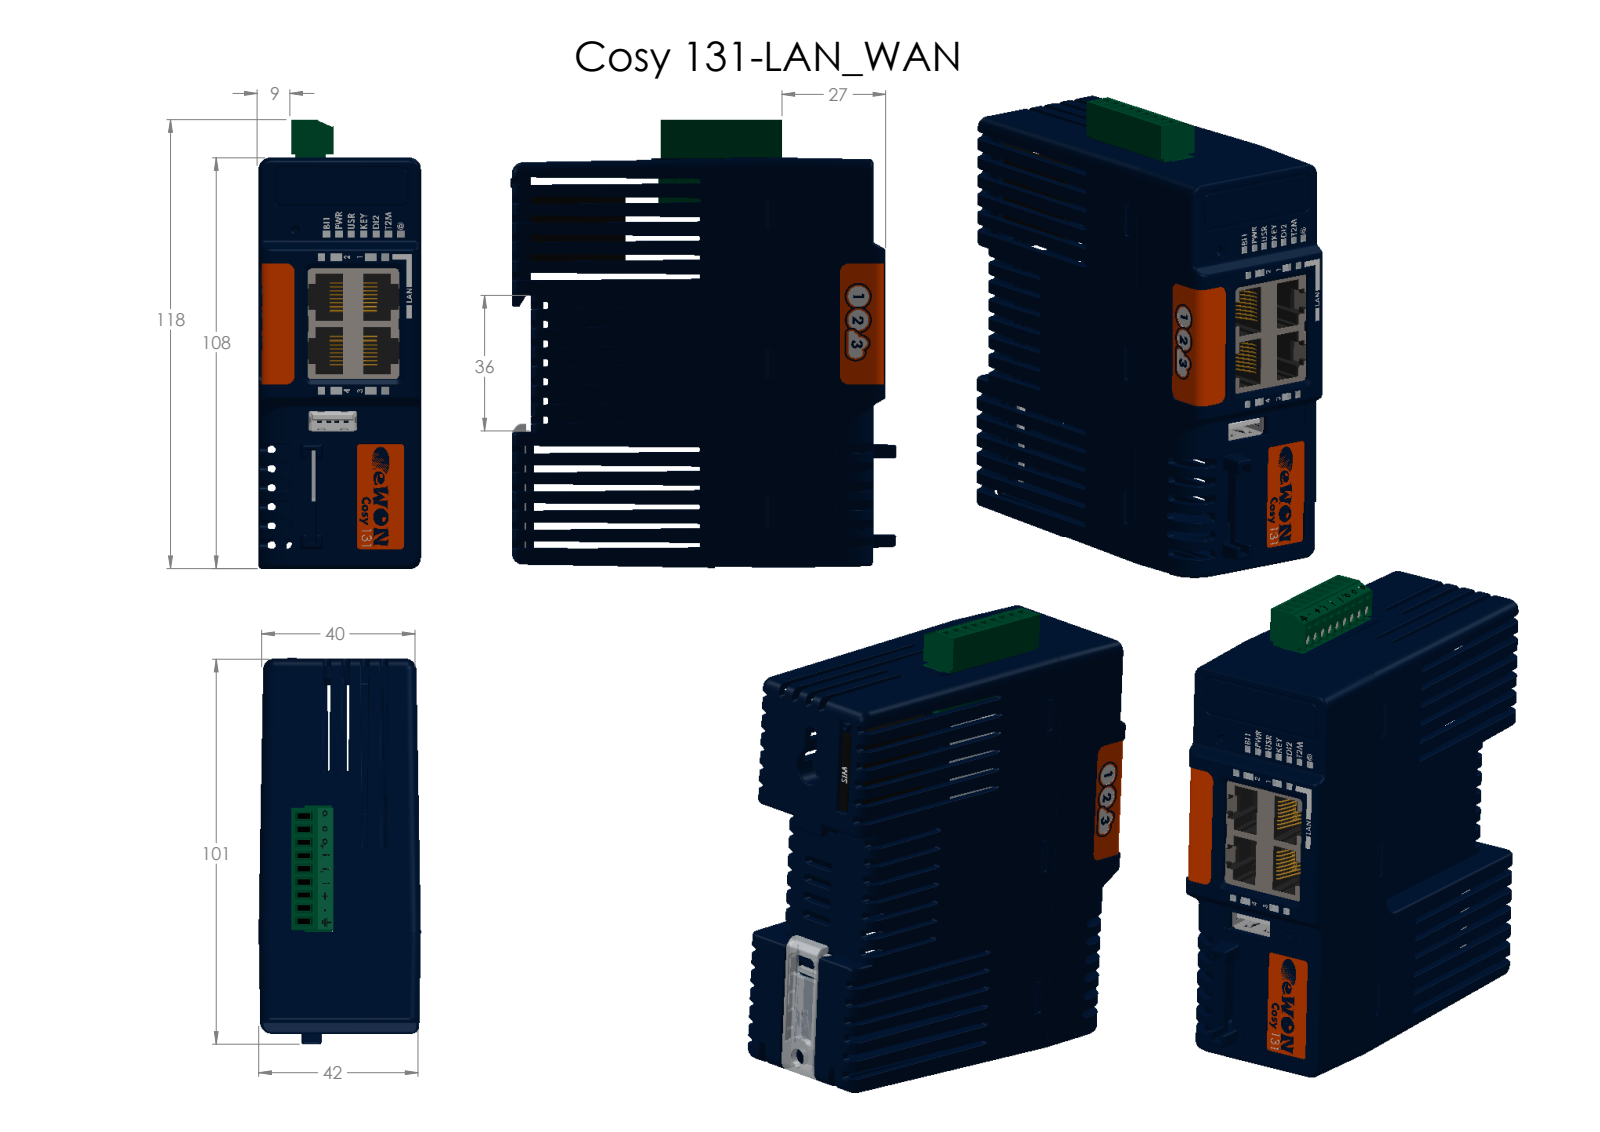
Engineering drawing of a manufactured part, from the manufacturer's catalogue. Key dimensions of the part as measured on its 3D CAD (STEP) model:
Part name (STEP PRODUCT): SIM Tray; COSY 131  LAN_WAN-WIFI_Ethernet COSY 131; DEFAULT-9; DEFAULT-2 (+8 more)
STEP written by: SolidWorks 2015 (AUTOMOTIVE_DESIGN)
Units: millimetres
Bodies: 68 solids, 6962 faces (4120 planar, 1634 cylindrical, 1208 other)
Overall size (bounding box): 117.78 × 101.28 × 42.64
Volume: 85 790 mm³ · Surface area: 126 542 mm²
Round holes (diameter × count): ⌀0.45 ×16, ⌀1 ×16, ⌀0.8 ×9, ⌀2 ×9, ⌀3 ×9, ⌀1.2 ×1, ⌀4.5 ×1, ⌀5.32 ×1, ⌀5.48 ×1, ⌀6 ×1, ⌀6.22 ×1, ⌀6.29 ×1
Round bosses / shafts (diameter × count): ⌀0.45 ×16, ⌀0.5 ×9, ⌀7.16 ×1, ⌀2.5 ×1, ⌀1.6 ×1, ⌀1.31 ×1
Partial cylindrical surfaces — rounded edges, fillets, slot ends (radius × count): R0.25 ×293, R0.5 ×133, R0.2 ×116, R1 ×80, R0.15 ×70, R0.75 ×26, R0.12 ×24, R0.23 ×24
Main face-to-face distances: 2, 5, 40.6, 7.08, 40.61, 10, 33.53, 3.25, 105.75, 93
Hole centre spacings: 3.5, 2.84, 7, 2.54, 10.5, 14, 5.08, 14.12
